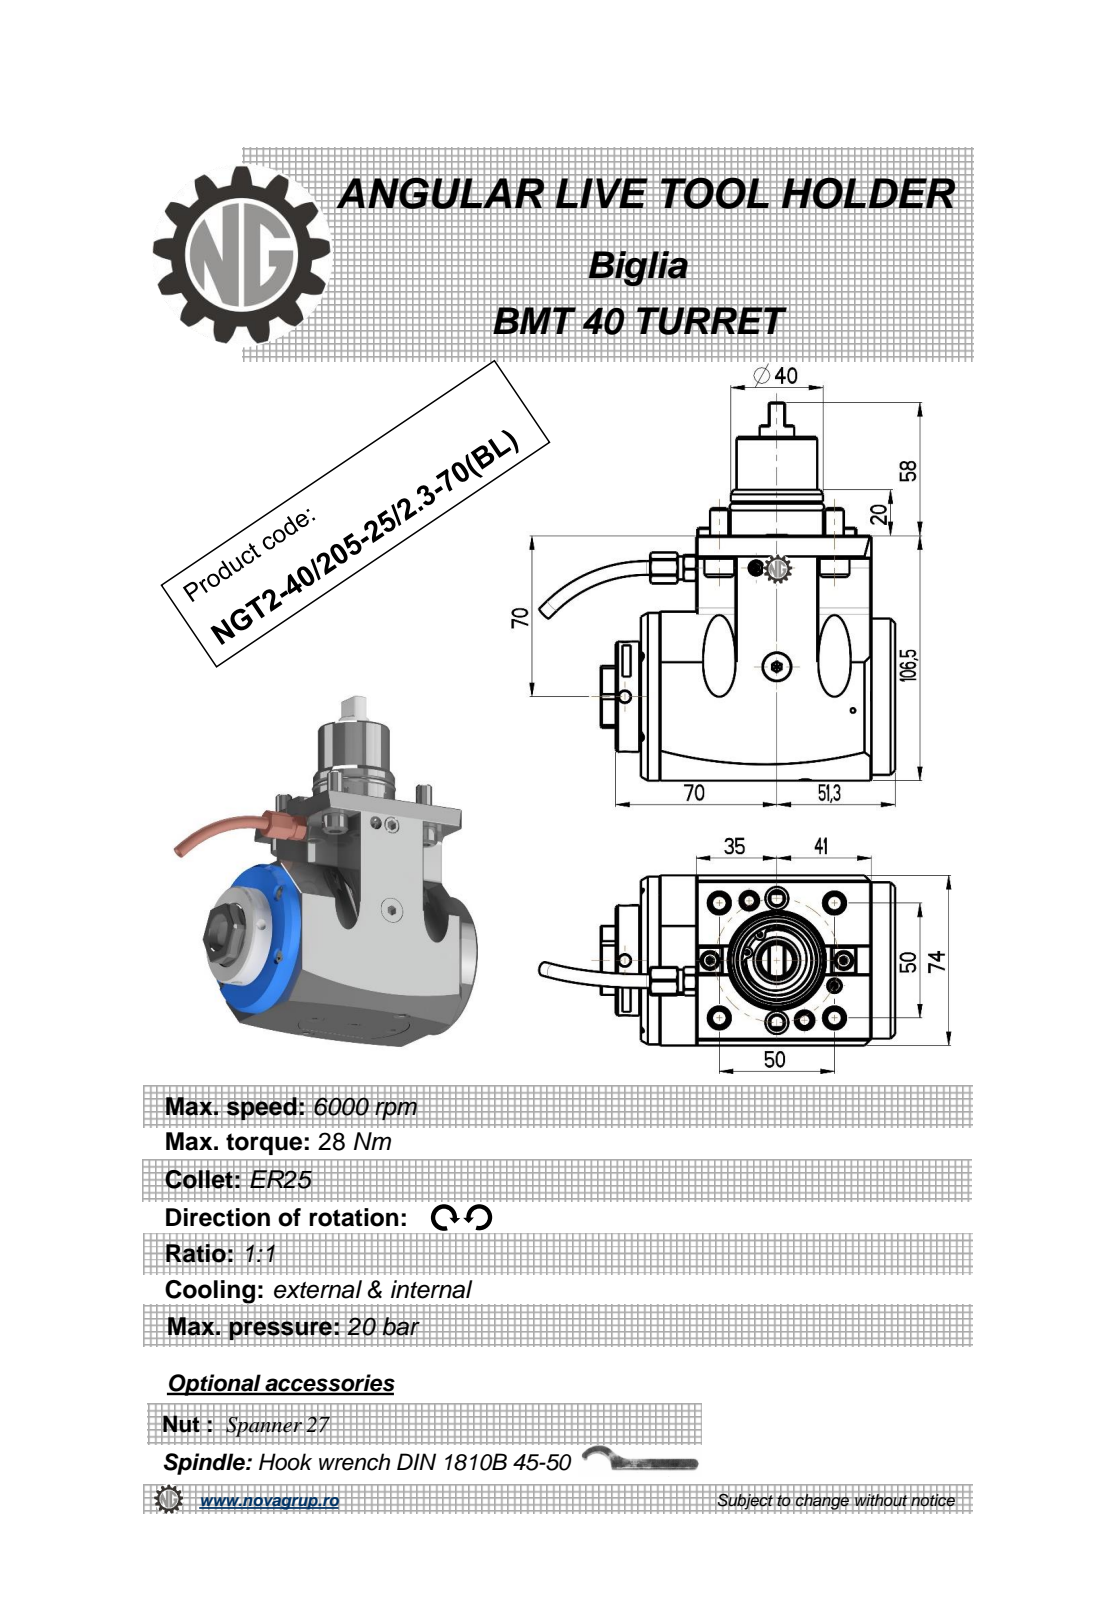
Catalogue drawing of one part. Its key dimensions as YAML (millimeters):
part_name: "NGT2_40_205_25_1_3_70_BL"
step_written_by: "PRO/ENGINEER BY PARAMETRIC TECHNOLOGY CORPORATION, 2010280 (CONFIG_CONTROL_DESIGN)"
units: millimeters
bodies: {solids: 1, faces: 412, planar: 194, cylindrical: 118, other: 100}
overall_size: [164.5, 154.47, 74]
volume: 749053
surface_area: 68571
round_holes:
  - {diameter: 4, count: 2}
  - {diameter: 5, count: 2}
  - {diameter: 6, count: 2}
  - {diameter: 18, count: 1}
  - {diameter: 26.5, count: 1}
round_bosses_or_shafts:
  - {diameter: 13, count: 4}
  - {diameter: 8, count: 4}
  - {diameter: 6, count: 2}
  - {diameter: 73, count: 1}
  - {diameter: 68, count: 1}
  - {diameter: 48, count: 1}
  - {diameter: 40, count: 1}
  - {diameter: 35.4, count: 1}
partial_cylinders:
  - {radius: 0.26, count: 20}
  - {radius: 4, count: 4}
  - {radius: 7, count: 4}
  - {radius: 0.8, count: 2}
  - {radius: 250, count: 2}
  - {radius: 6.25, count: 1}
  - {radius: 6.75, count: 1}
  - {radius: 15, count: 1}
face_to_face_distances: [74, 106.5, 52, 10.3, 53, 23, 100, 110.3, 76, 59]
hole_center_spacings: [71.31, 54, 56.72]
